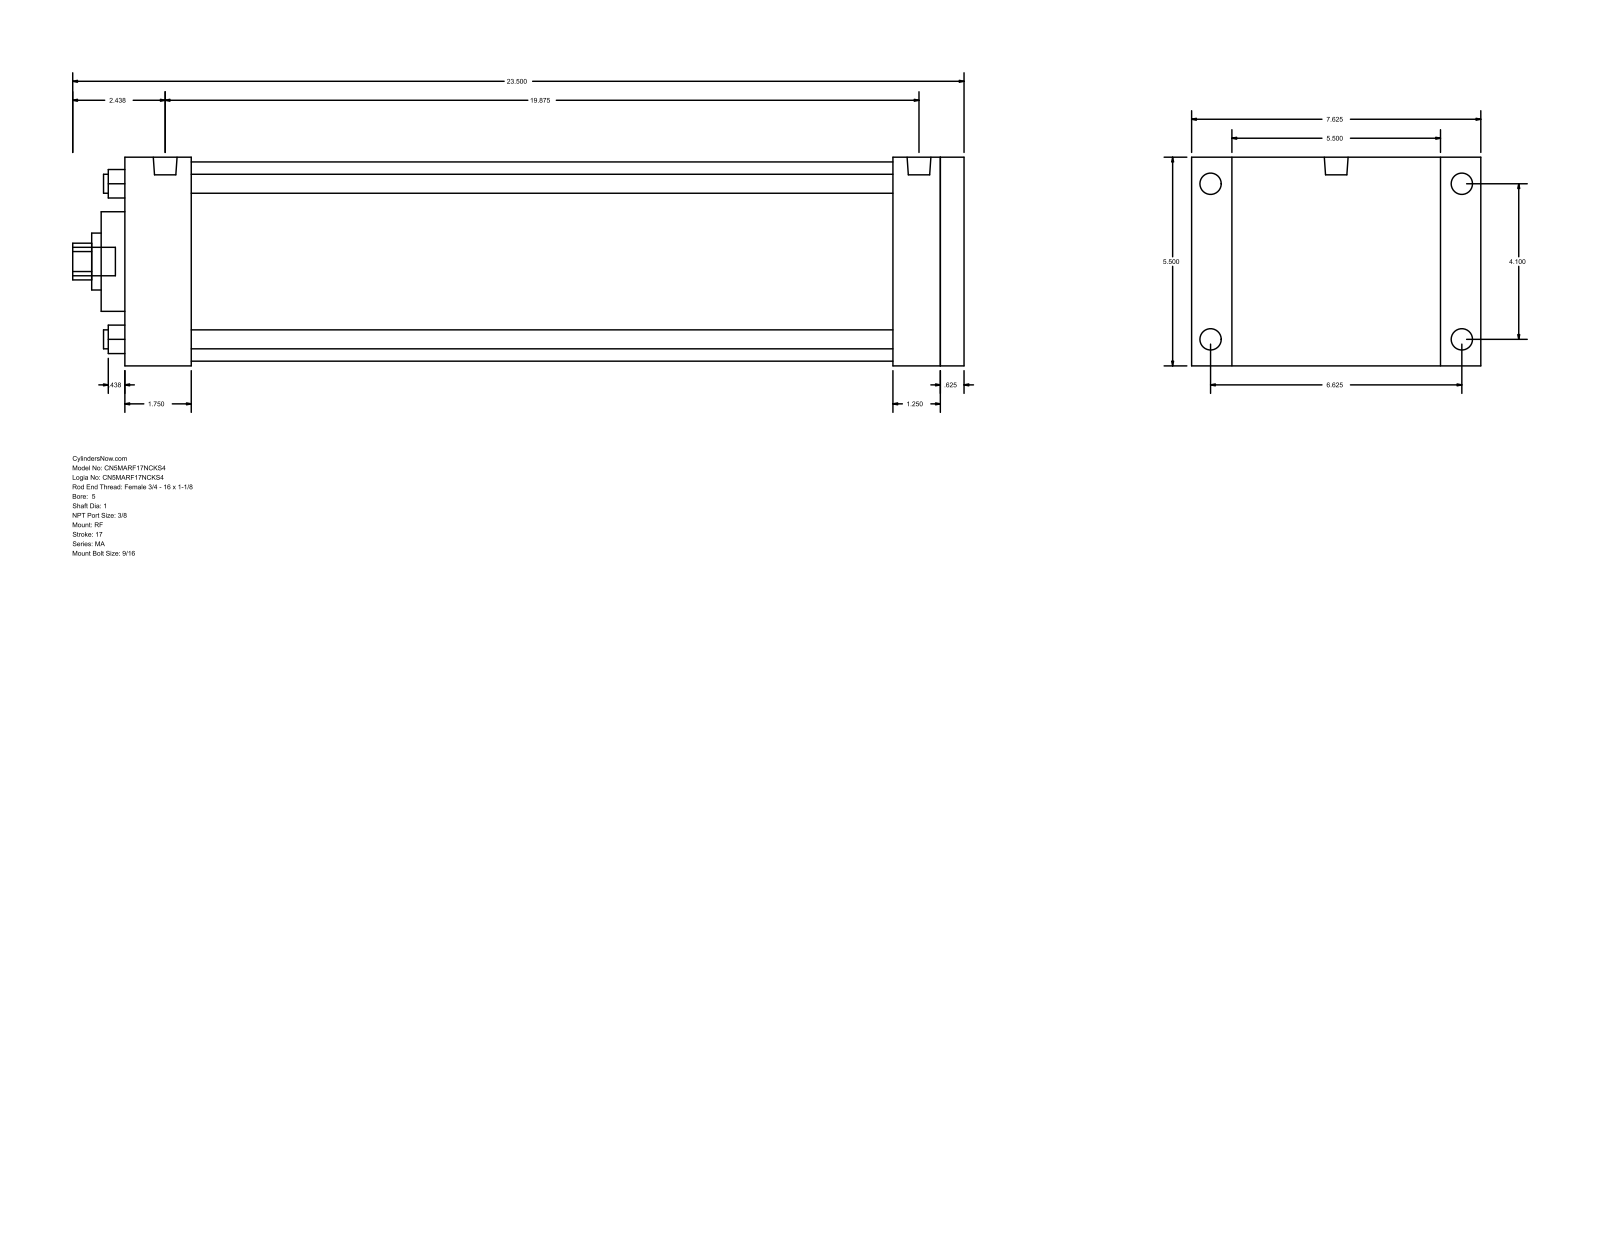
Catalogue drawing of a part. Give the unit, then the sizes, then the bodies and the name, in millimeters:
Units: millimetres
Overall size (bounding box): 596.9 × 193.68 × 139.7
Round holes (diameter × count): ⌀12.7 ×4, ⌀25.4 ×1, ⌀38.1 ×1, ⌀66.67 ×1, ⌀133.35 ×1
Round bosses / shafts (diameter × count): ⌀14.29 ×4, ⌀11.11 ×4, ⌀15.93 ×2, ⌀19.05 ×1
Partial cylindrical surfaces — rounded edges, fillets, slot ends (radius × count): R12.29 ×1
Main face-to-face distances: 139.7, 561.98, 546.1, 15.88, 44.46, 501.64, 517.52, 514.35, 469.89, 31.75
Hole centre spacings: 73.64, 104.14, 147.28
Bodies: 0 solids, 94 faces (65 planar, 29 cylindrical, 0 other)
Part name (STEP PRODUCT): MA_RF__0500_1
STEP written by: GSSL Pune (CONFIG_CONTROL_DESIGN)
